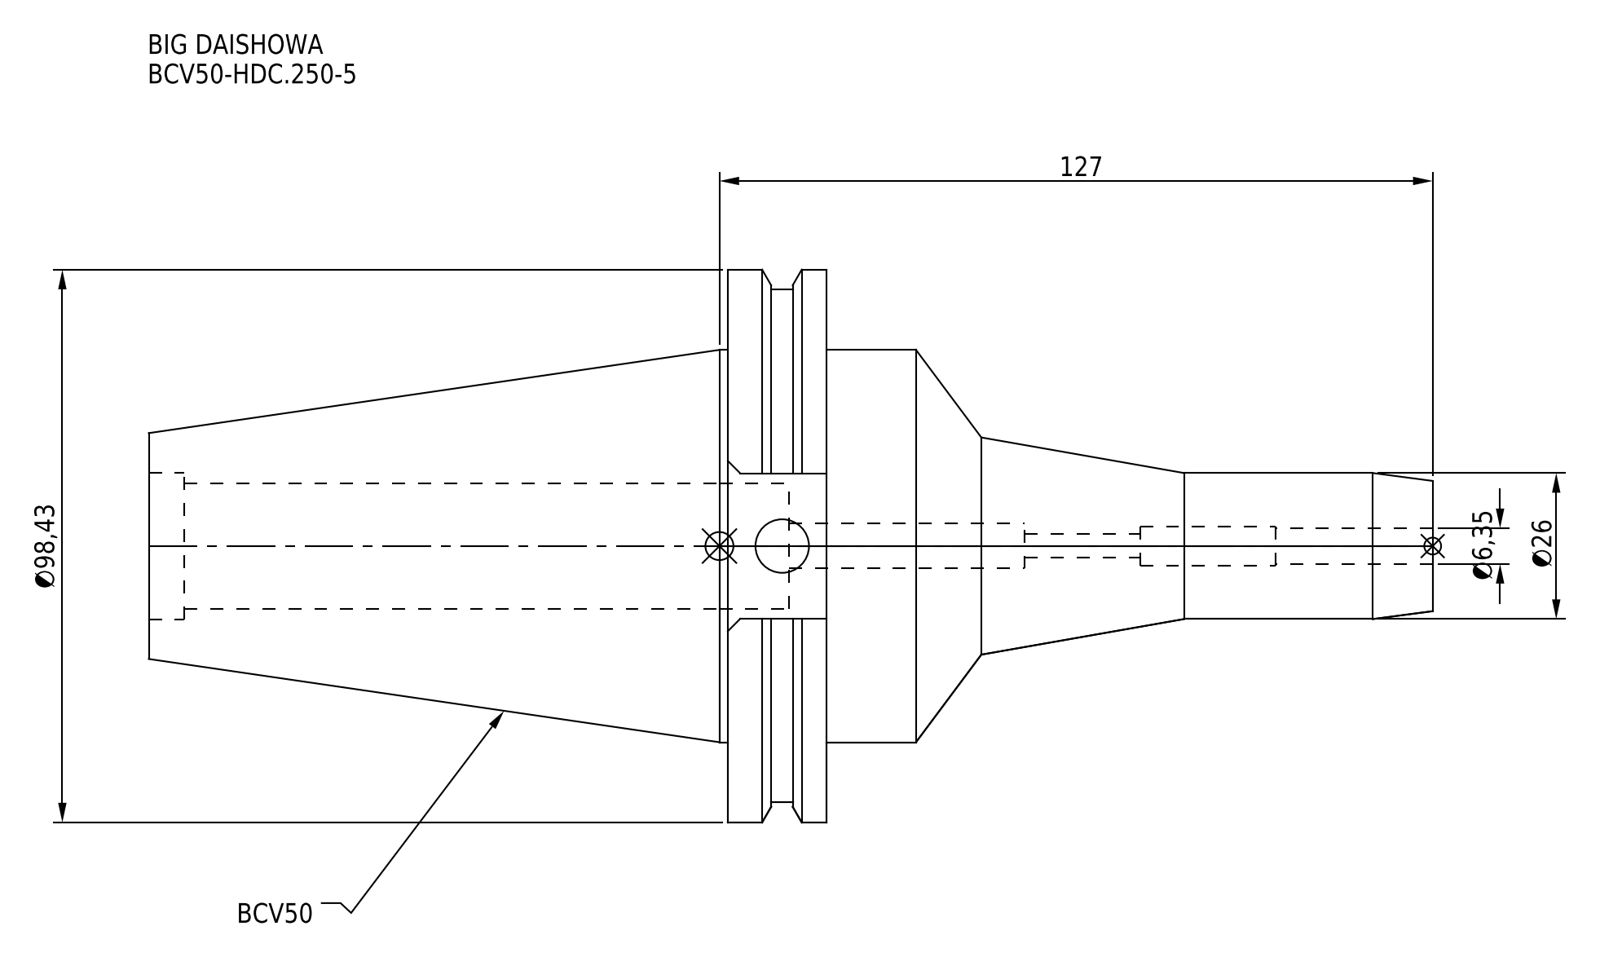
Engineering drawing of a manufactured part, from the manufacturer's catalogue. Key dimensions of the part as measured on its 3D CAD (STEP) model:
Part name (STEP PRODUCT): BCV50-HDC_250-5
STEP written by: CREO PARAMETRIC BY PTC INC, 2016380 (AUTOMOTIVE_DESIGN)
Units: millimetres
Bodies: 1 solid, 64 faces (24 planar, 28 cylindrical, 12 other)
Overall size (bounding box): 228.6 × 98.42 × 94.95
Volume: 463 143 mm³ · Surface area: 57 756 mm²
Round holes (diameter × count): ⌀4.2 ×1, ⌀6.35 ×1, ⌀6.9 ×1, ⌀8 ×1, ⌀9.53 ×1, ⌀22.3 ×1, ⌀26.23 ×1
Round bosses / shafts (diameter × count): ⌀98.42 ×1, ⌀91.29 ×1, ⌀69.85 ×1, ⌀26 ×1
Main face-to-face distances: 17.55, 120.65, 103.1, 107.95, 125.5, 228.6, 72.95, 114.6, 6.65, 10.9
